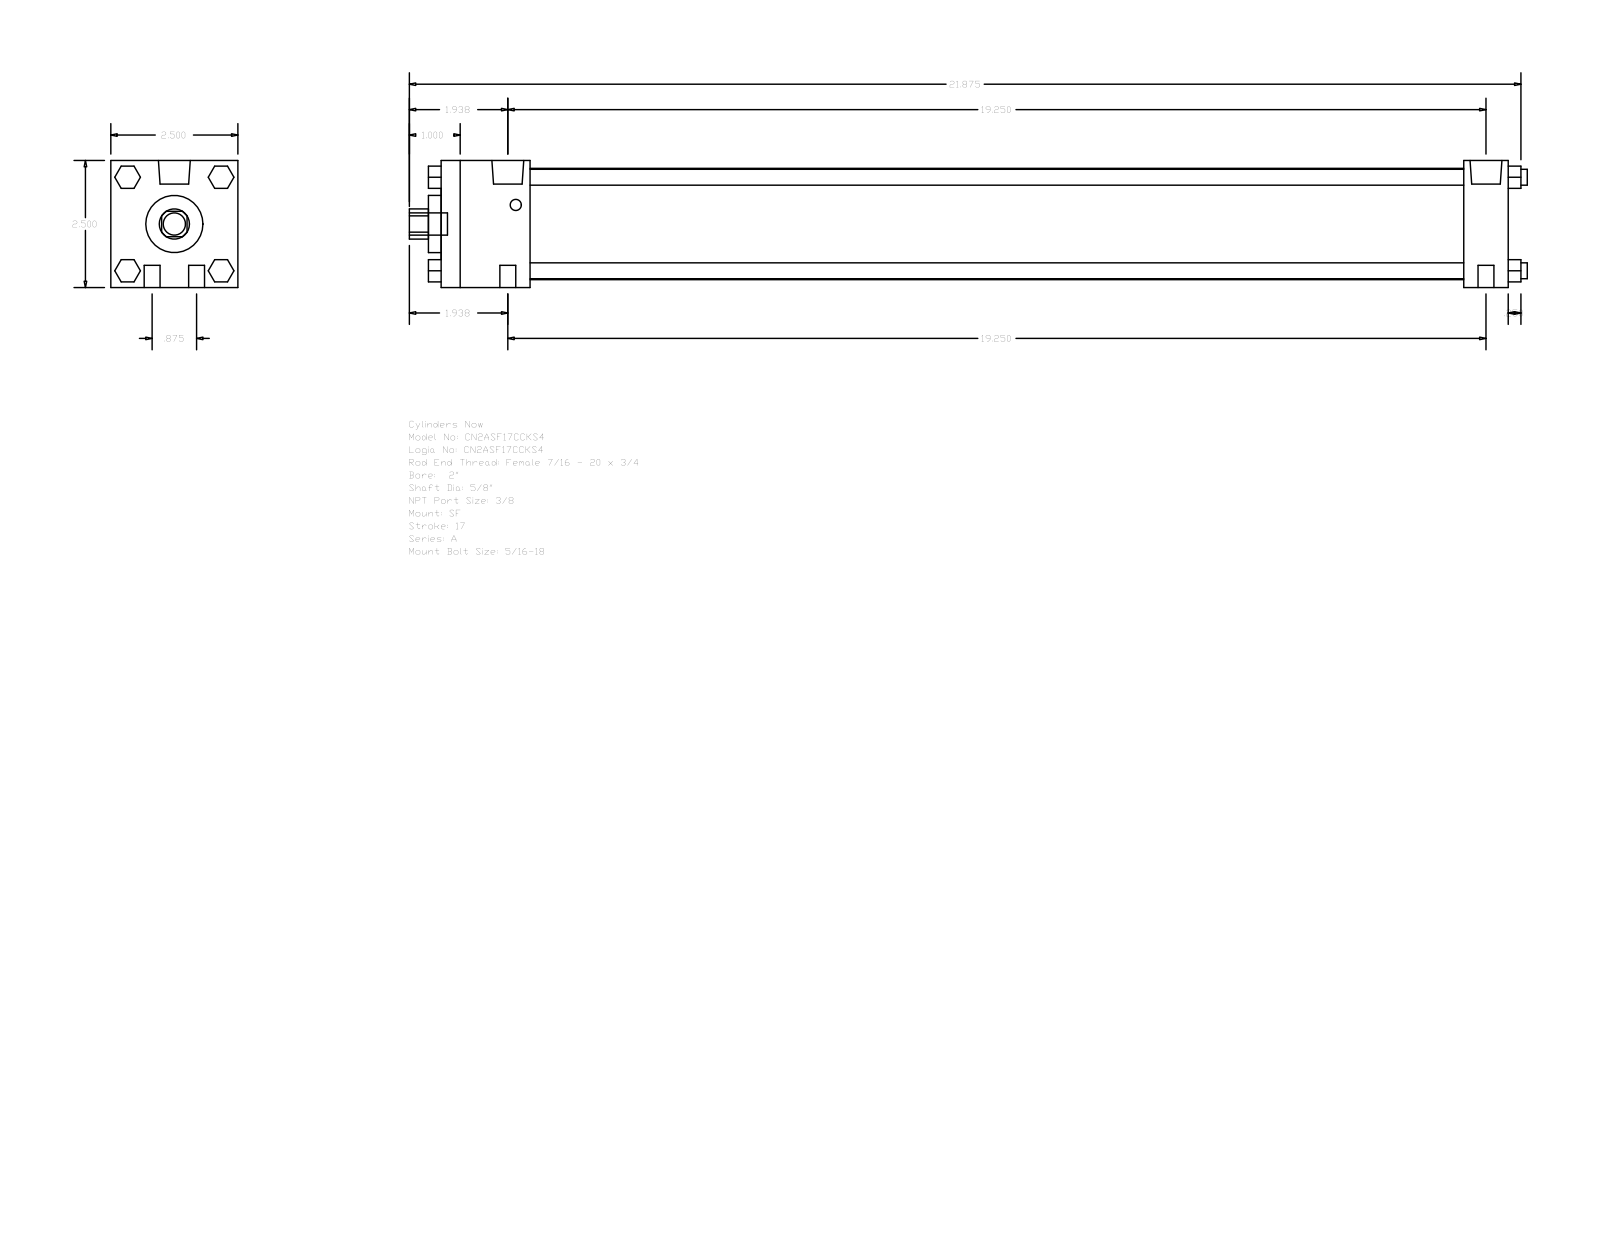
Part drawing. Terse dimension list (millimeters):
name: A_SF__0200_0.625
written by: GSSL Pune (CONFIG_CONTROL_DESIGN)
unit: mm
bodies: 0 solids, 124 faces (94 planar, 30 cylindrical, 0 other)
size: 558.8 × 63.5 × 63.5
holes: 1× ⌀15.88, 1× ⌀28.57, 1× ⌀55.63
bosses: 8× ⌀7.94, 2× ⌀15.93, 2× ⌀5.56, 1× ⌀11.11
rounds: 1× R7.54
face distances: 63.5, 533.39, 511.17, 22.22, 44.45, 466.72, 488.94, 6.35, 539.74, 50.8
